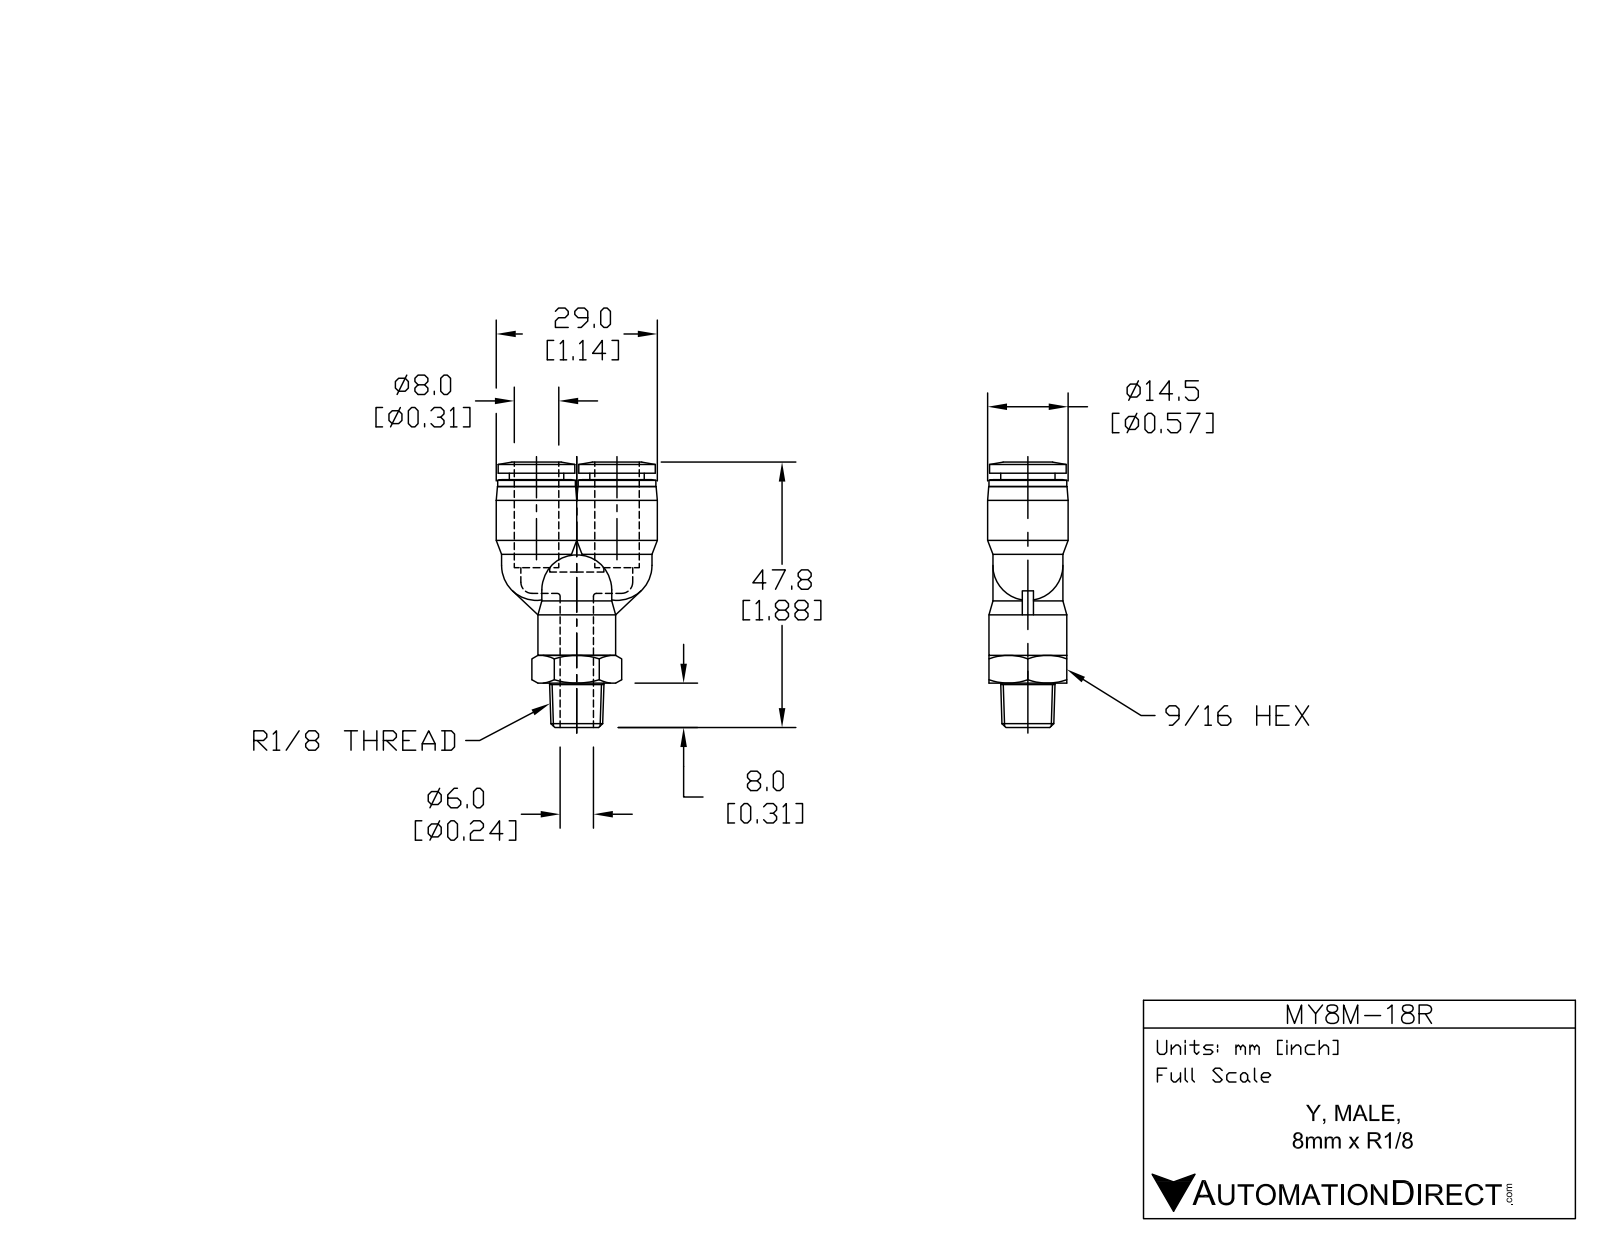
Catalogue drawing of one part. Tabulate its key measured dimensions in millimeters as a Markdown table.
| quantity | value |
| --- | --- |
| part name | MY8M-18R |
| STEP written by | SolidWorks 2015 (AUTOMOTIVE_DESIGN) |
| units | millimeters |
| bodies | 1 solid, 105 faces (23 planar, 35 cylindrical, 47 other) |
| overall size | 47.4 × 29 × 14.5 |
| volume | 6 750 mm³ |
| surface area | 5 306 mm² |
| round holes (diameter × count) | 6 × 4, 8.3 × 2 |
| round bosses / shafts (diameter × count) | 14 × 3, 12.6 × 3, 14.5 × 2, 13.8 × 2, 9.8 × 2 |
| main face-to-face distances | 14, 1.1, 36.2, 37.4, 20.8, 15.4, 16.6, 8, 2, 6 |
| hole center spacings | 7.2, 14.5 |
